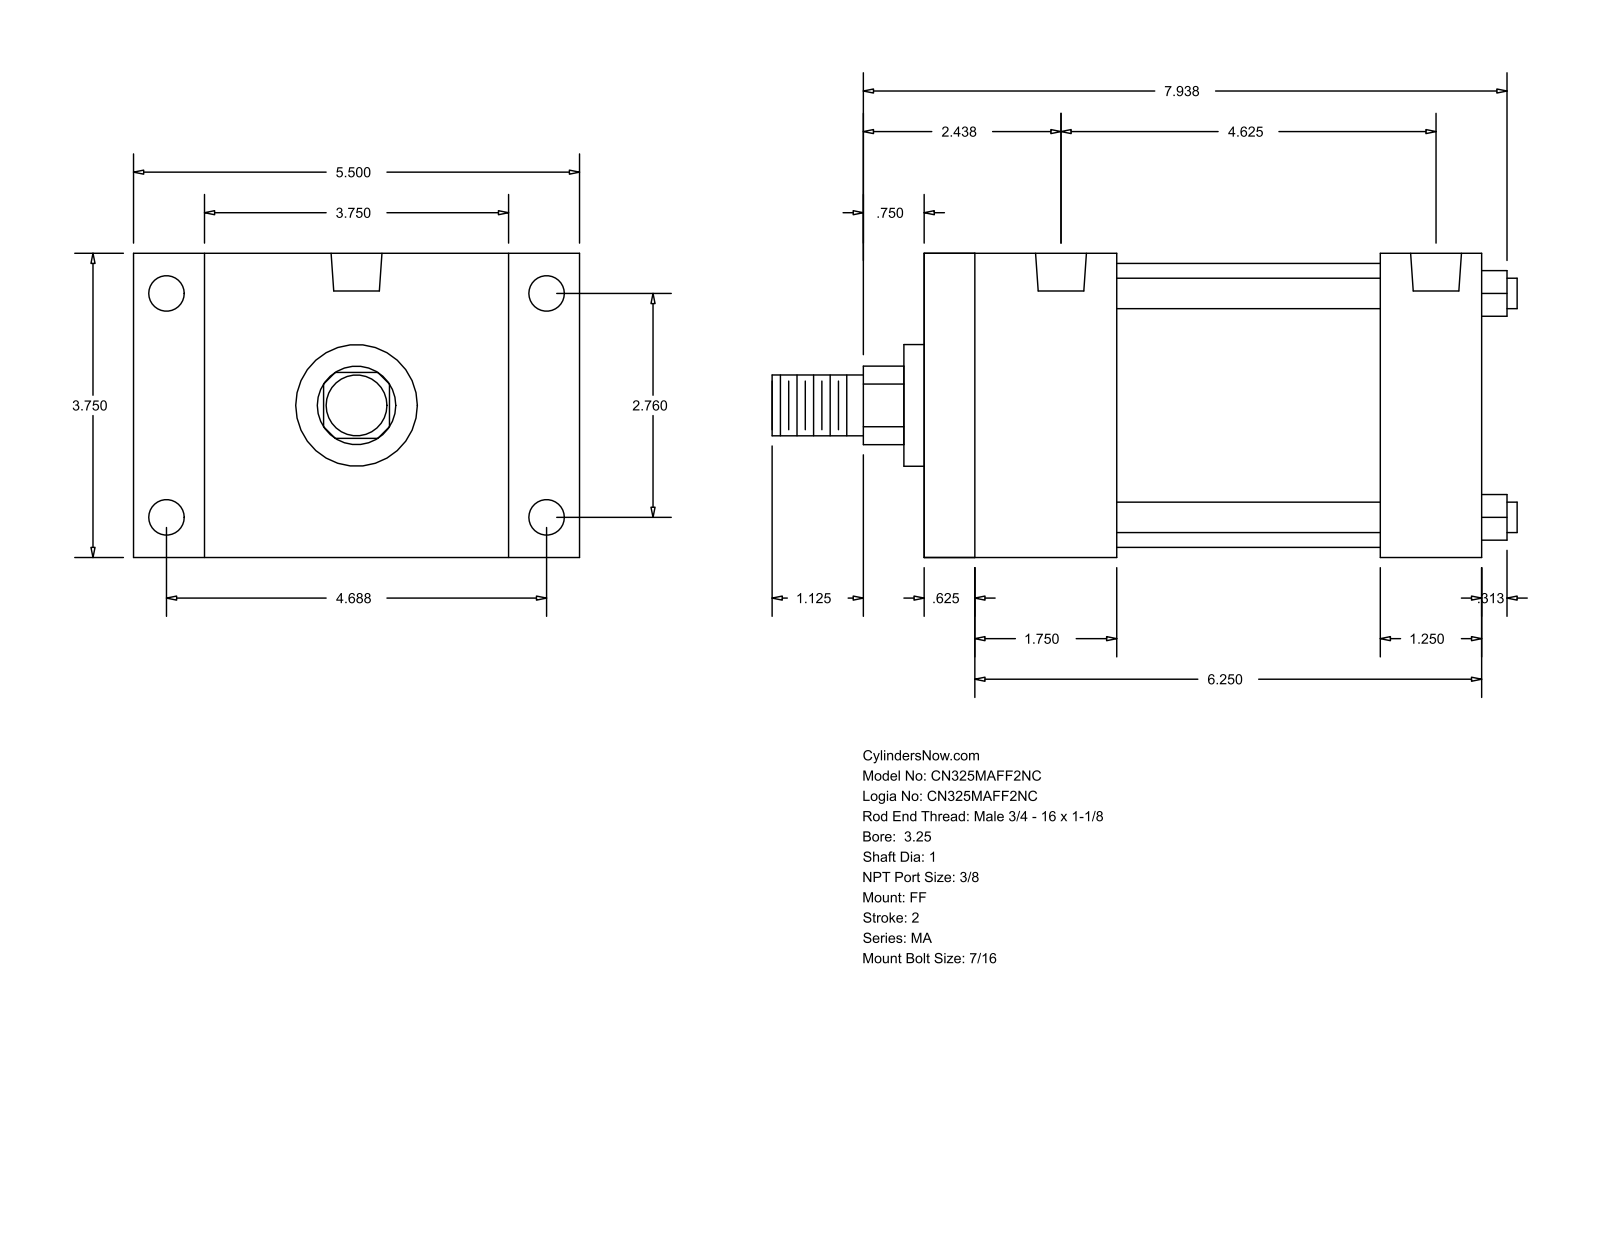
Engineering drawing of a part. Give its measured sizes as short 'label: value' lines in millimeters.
name: MA_FF__0325_1
written by: GSSL Pune (CONFIG_CONTROL_DESIGN)
unit: mm
bodies: 0 solids, 92 faces (64 planar, 28 cylindrical, 0 other)
size: 233.36 × 139.7 × 95.25
holes: 8× ⌀11.11, 2× ⌀15.93
bosses: 4× ⌀9.53, 1× ⌀88.9, 1× ⌀38.1, 1× ⌀25.4, 1× ⌀19.05
rounds: 1× R12.29
face distances: 95.24, 174.63, 15.87, 158.76, 22.23, 117.47, 60.33, 142.88, 44.46, 127.01
hole spacings: 70.1, 107.95, 119.06, 138.16, 4.76, 4.77, 112.71, 112.72
